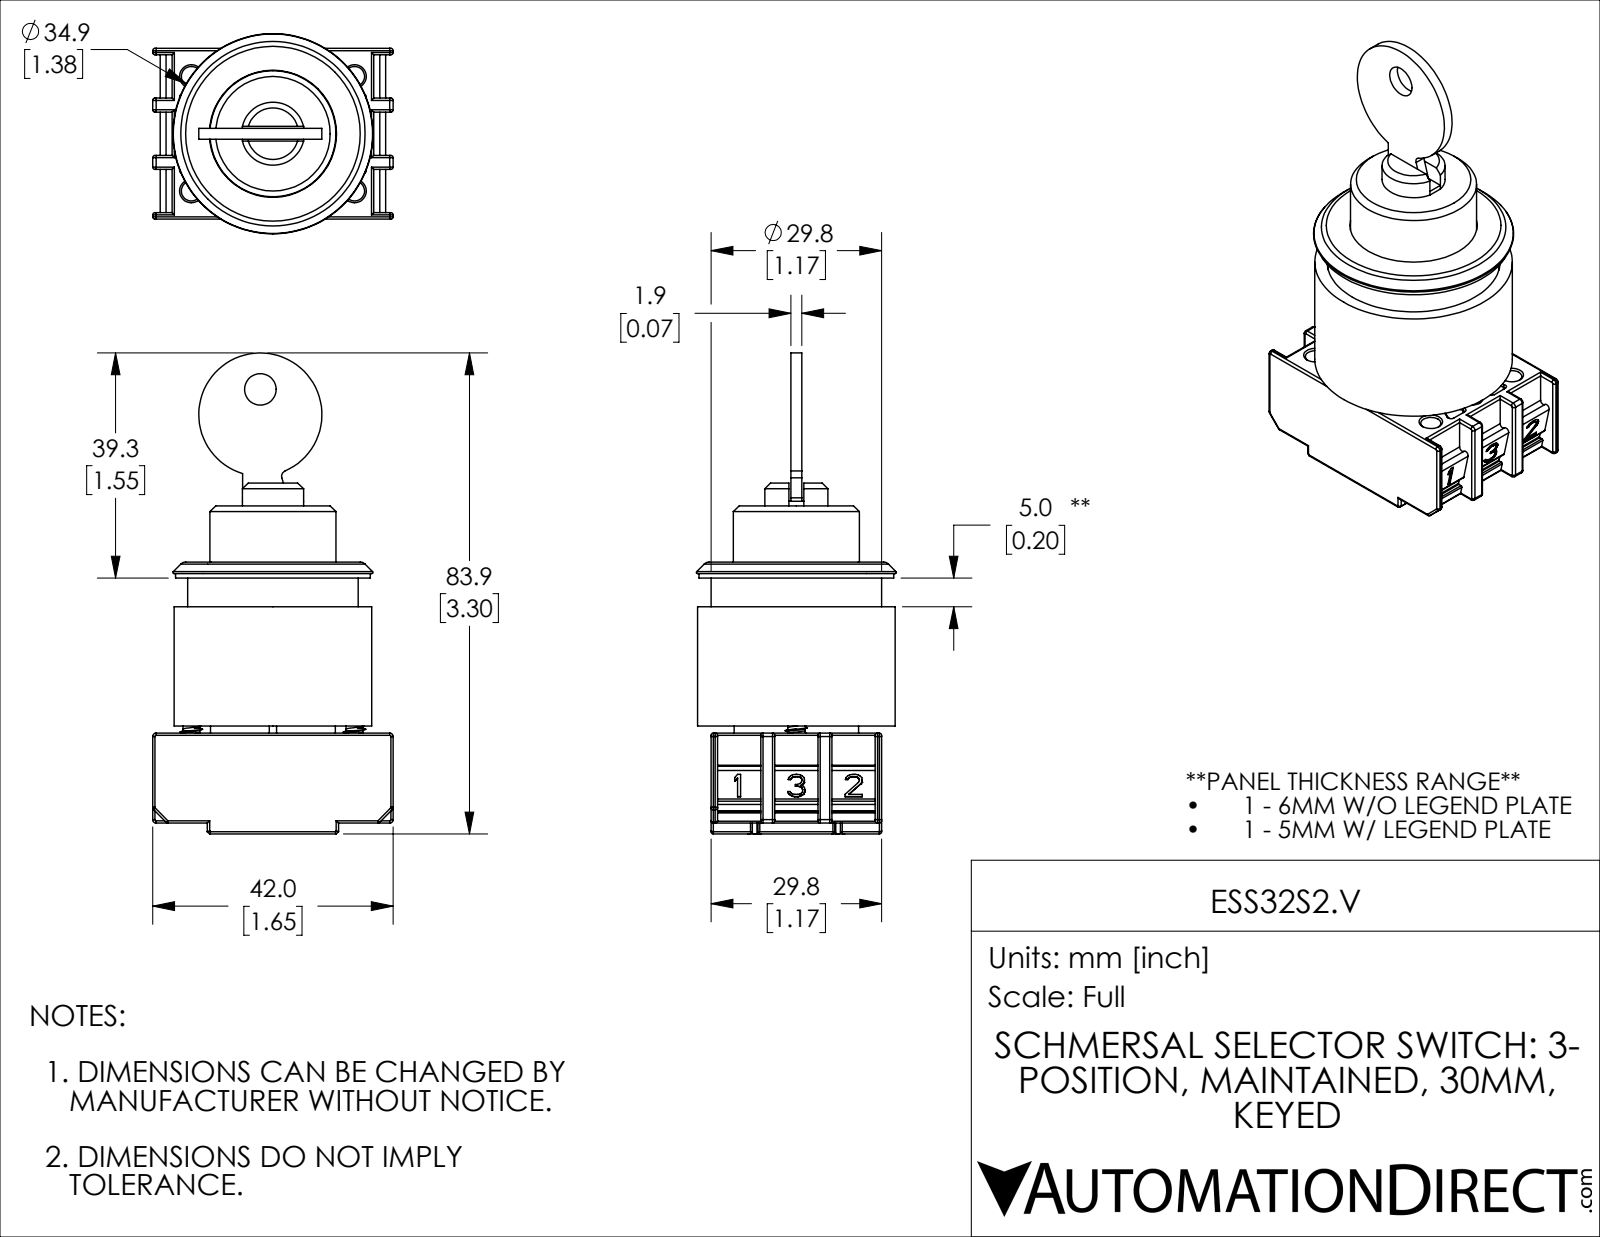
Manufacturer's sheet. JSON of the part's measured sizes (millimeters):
{"part_name": "ESS32S2.V", "step_written_by": "SolidWorks 2019 (CONFIG_CONTROL_DESIGN)", "units": "millimeters", "bodies": {"solids": 6, "faces": 1565, "planar": 586, "cylindrical": 551, "other": 428}, "overall_size": [83.94, 42, 34.93], "volume_mm3": 36829, "surface_area_mm2": 27554, "round_holes": [[3.5, 10], [5.15, 6], [5, 4], [2, 3], [2.5, 2], [2.8, 2], [3, 1], [5.5, 1], [12.1, 1], [12.5, 1], [14, 1], [19, 1]], "round_bosses_or_shafts": [[4.8, 2], [2.93, 2], [34.5, 1], [34, 1], [29.8, 1], [25.5, 1], [22, 1], [21.8, 1]], "partial_cylinders_radius": [[0.4, 120], [0.3, 48], [0.2, 28], [0.6, 8], [0.5, 7], [0.8, 6], [0.1, 2], [0.6, 2]], "face_to_face_distances": [16.1, 13.95, 15.85, 29.8, 1.9, 17.6, 17.35, 18.85, 39.65, 10], "hole_center_spacings": [9.94, 4.24, 4.75, 6, 8.69, 8.99, 10, 10.13]}
